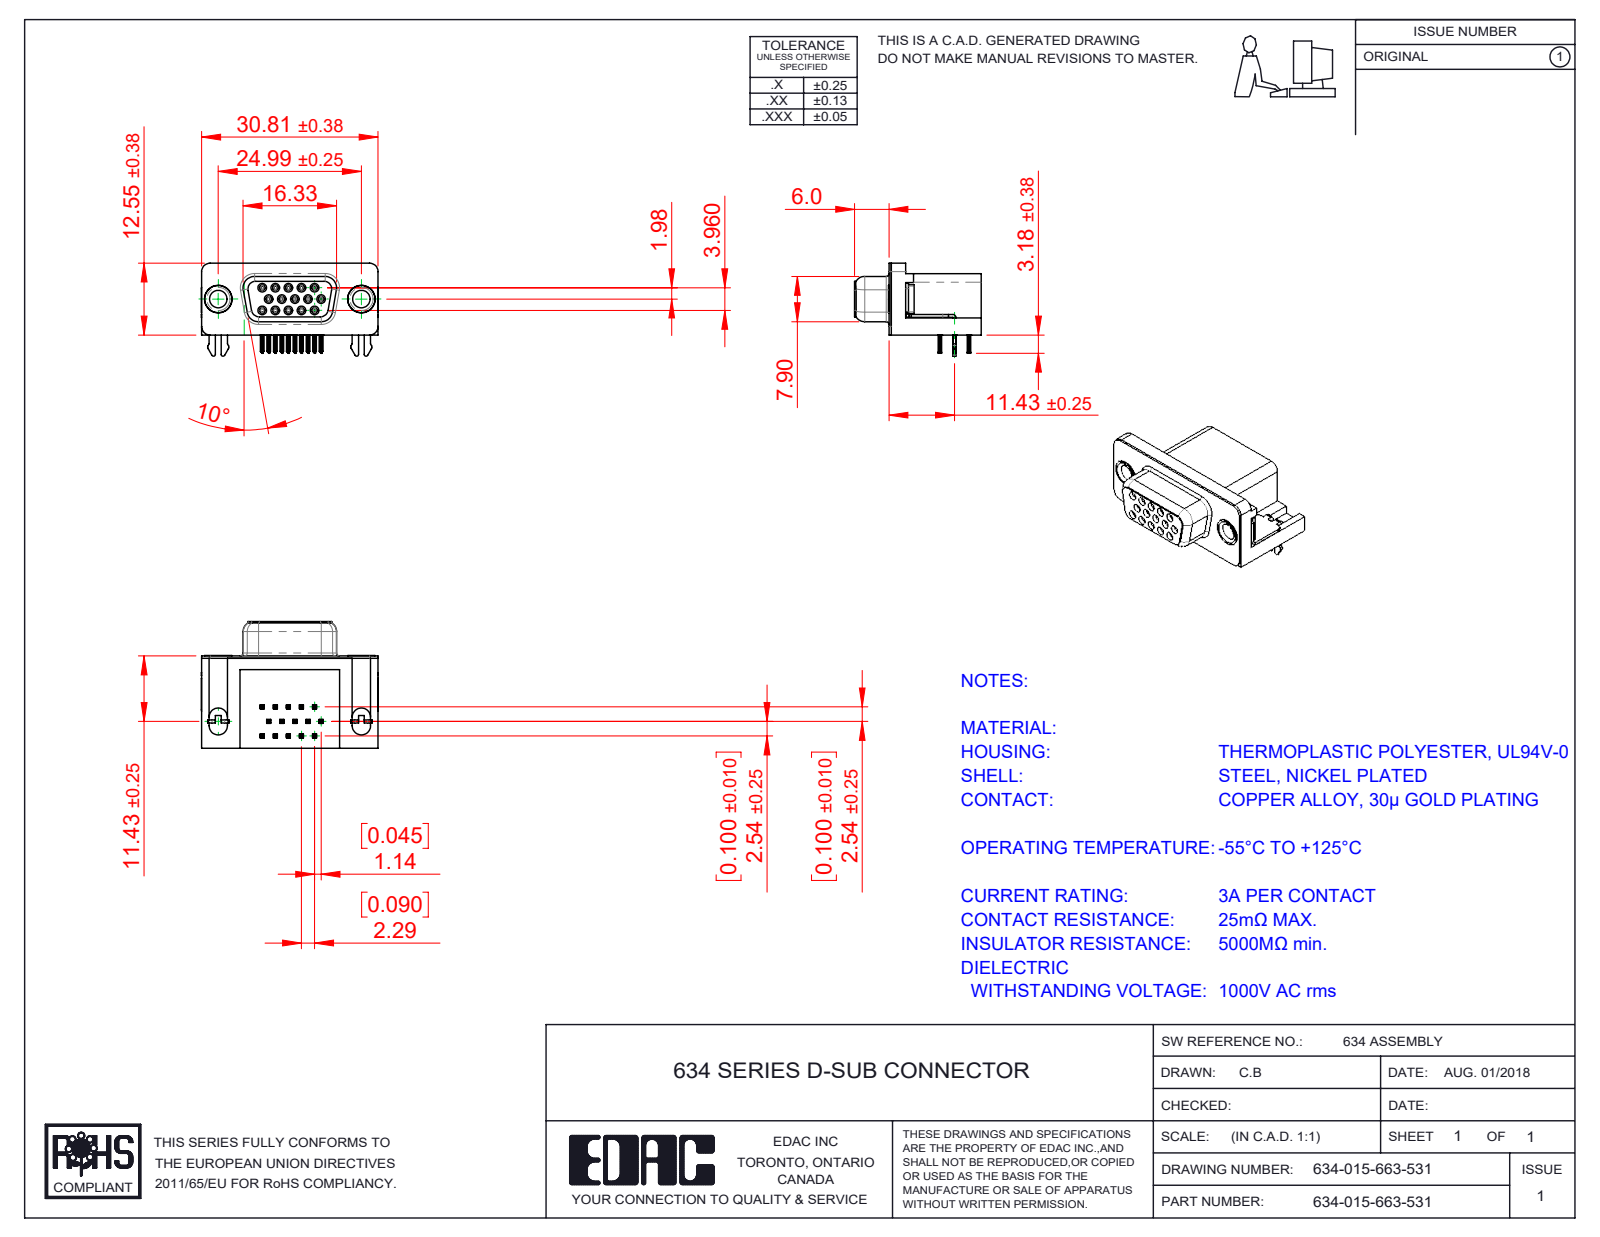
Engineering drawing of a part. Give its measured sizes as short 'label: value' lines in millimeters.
name: 634 Housing; 2 Prong Board Lock; Contact Top; Contact Bottom (+4 more)
written by: SolidWorks 2016 (CONFIG_CONTROL_DESIGN)
unit: mm
bodies: 21 solids, 2421 faces (1098 planar, 589 cylindrical, 734 other)
size: 30.89 × 22.1 × 16.25
volume: 4 541 mm³; area: 6 487 mm²
holes: 15× ⌀0.8, 15× ⌀0.9, 2× ⌀3.05, 2× ⌀4, 2× ⌀4.8, 2× ⌀5
bosses: 15× ⌀1.2, 2× ⌀4.9, 2× ⌀4.75, 2× ⌀3.85
rounds: 120× R0.1, 60× R0.15, 30× R0.35, 19× R1, 15× R0.34, 10× R0.5, 8× R0.25, 8× R1.35
face distances: 0.4, 10.35, 15.7, 16.1, 0.35, 2.5, 2.9, 6.4, 0.5, 0.6
hole spacings: 2.29, 2.28, 3.96, 4.57, 6.05, 3.97, 4.58, 6.86
